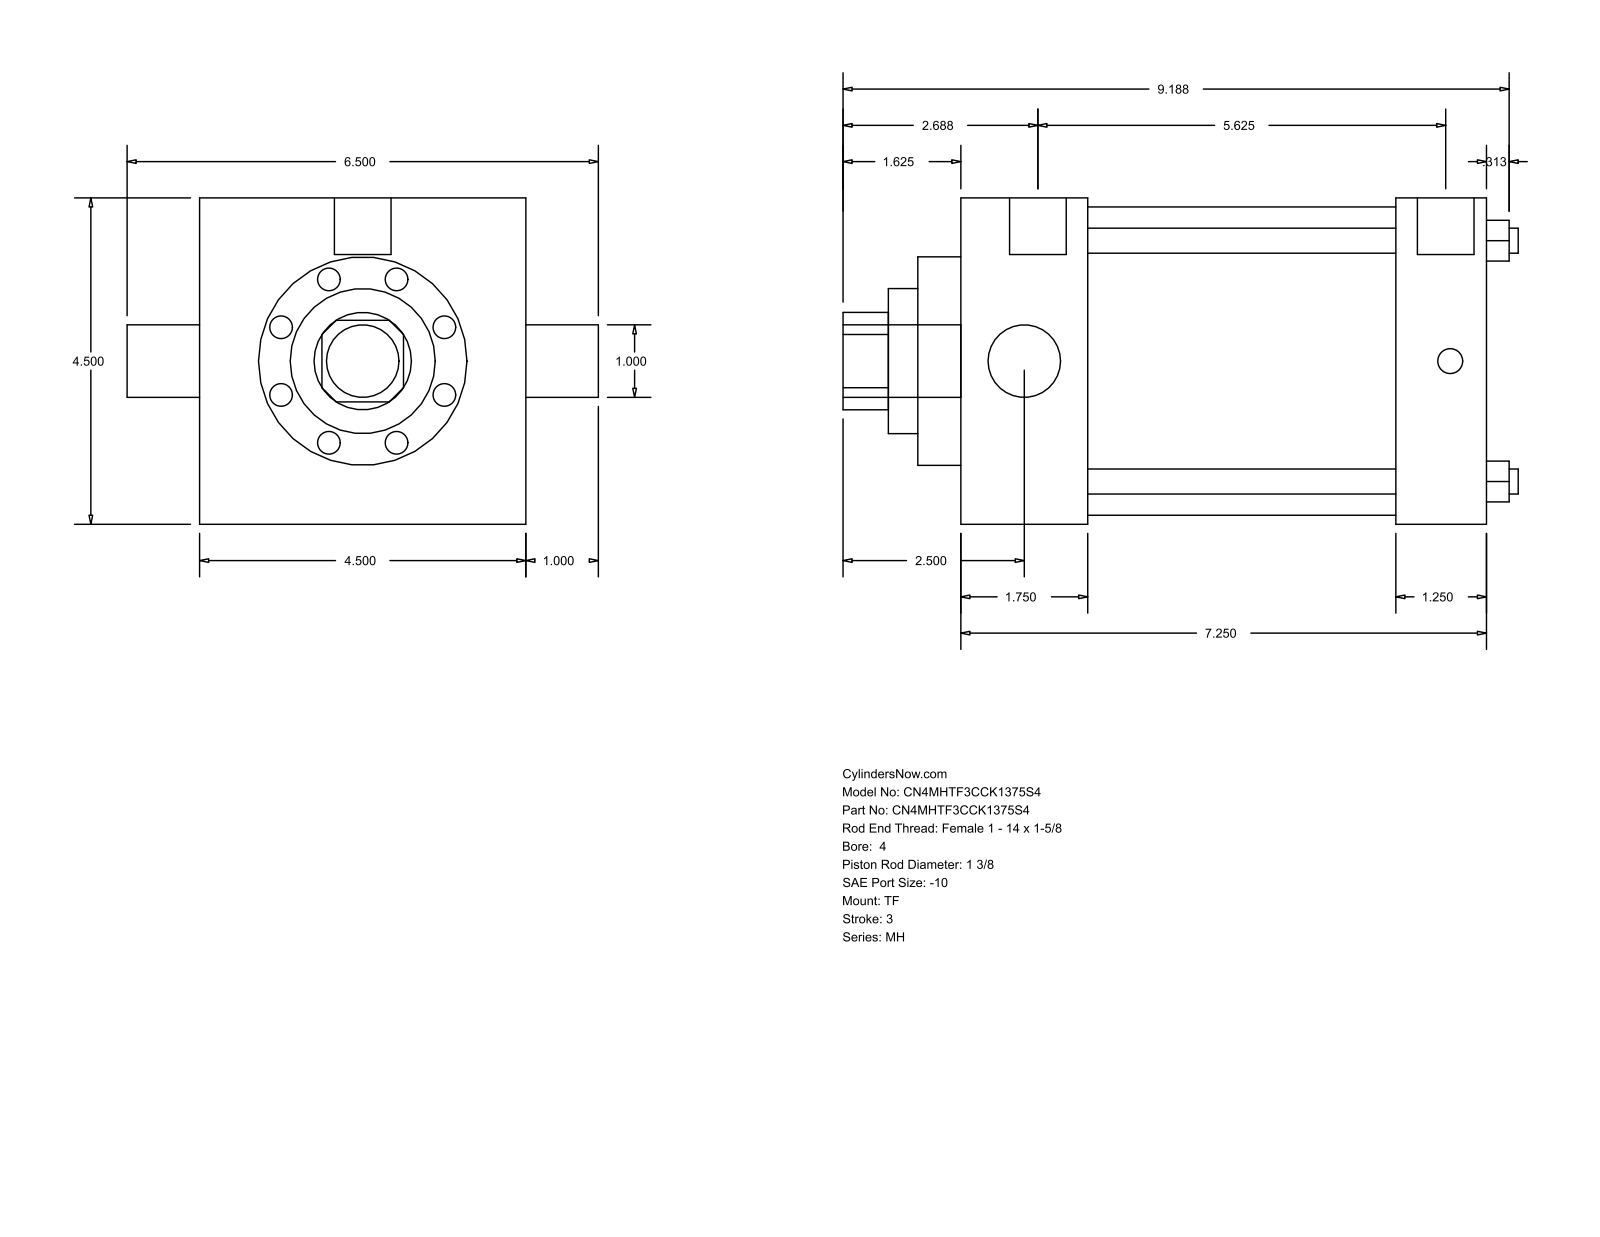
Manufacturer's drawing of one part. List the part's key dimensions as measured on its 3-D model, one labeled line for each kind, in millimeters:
Part name (STEP PRODUCT): MH_TF__0400_1.375
STEP written by: GSSL Pune (CONFIG_CONTROL_DESIGN)
Units: millimetres
Bodies: 0 solids, 86 faces (61 planar, 25 cylindrical, 0 other)
Overall size (bounding box): 236.54 × 165.1 × 114.3
Round holes (diameter × count): ⌀8.76 ×4, ⌀25.4 ×1, ⌀34.92 ×1, ⌀50.8 ×1, ⌀73.03 ×1, ⌀107.95 ×1
Round bosses / shafts (diameter × count): ⌀8.73 ×3, ⌀19.84 ×2, ⌀25.4 ×1
Partial cylindrical surfaces — rounded edges, fillets, slot ends (radius × count): R17.06 ×1
Main face-to-face distances: 114.3, 184.16, 44.45, 139.71, 152.41, 107.96, 31.75, 15.08, 59.53, 167.49
Hole centre spacings: 59.62, 84.32, 119.25
